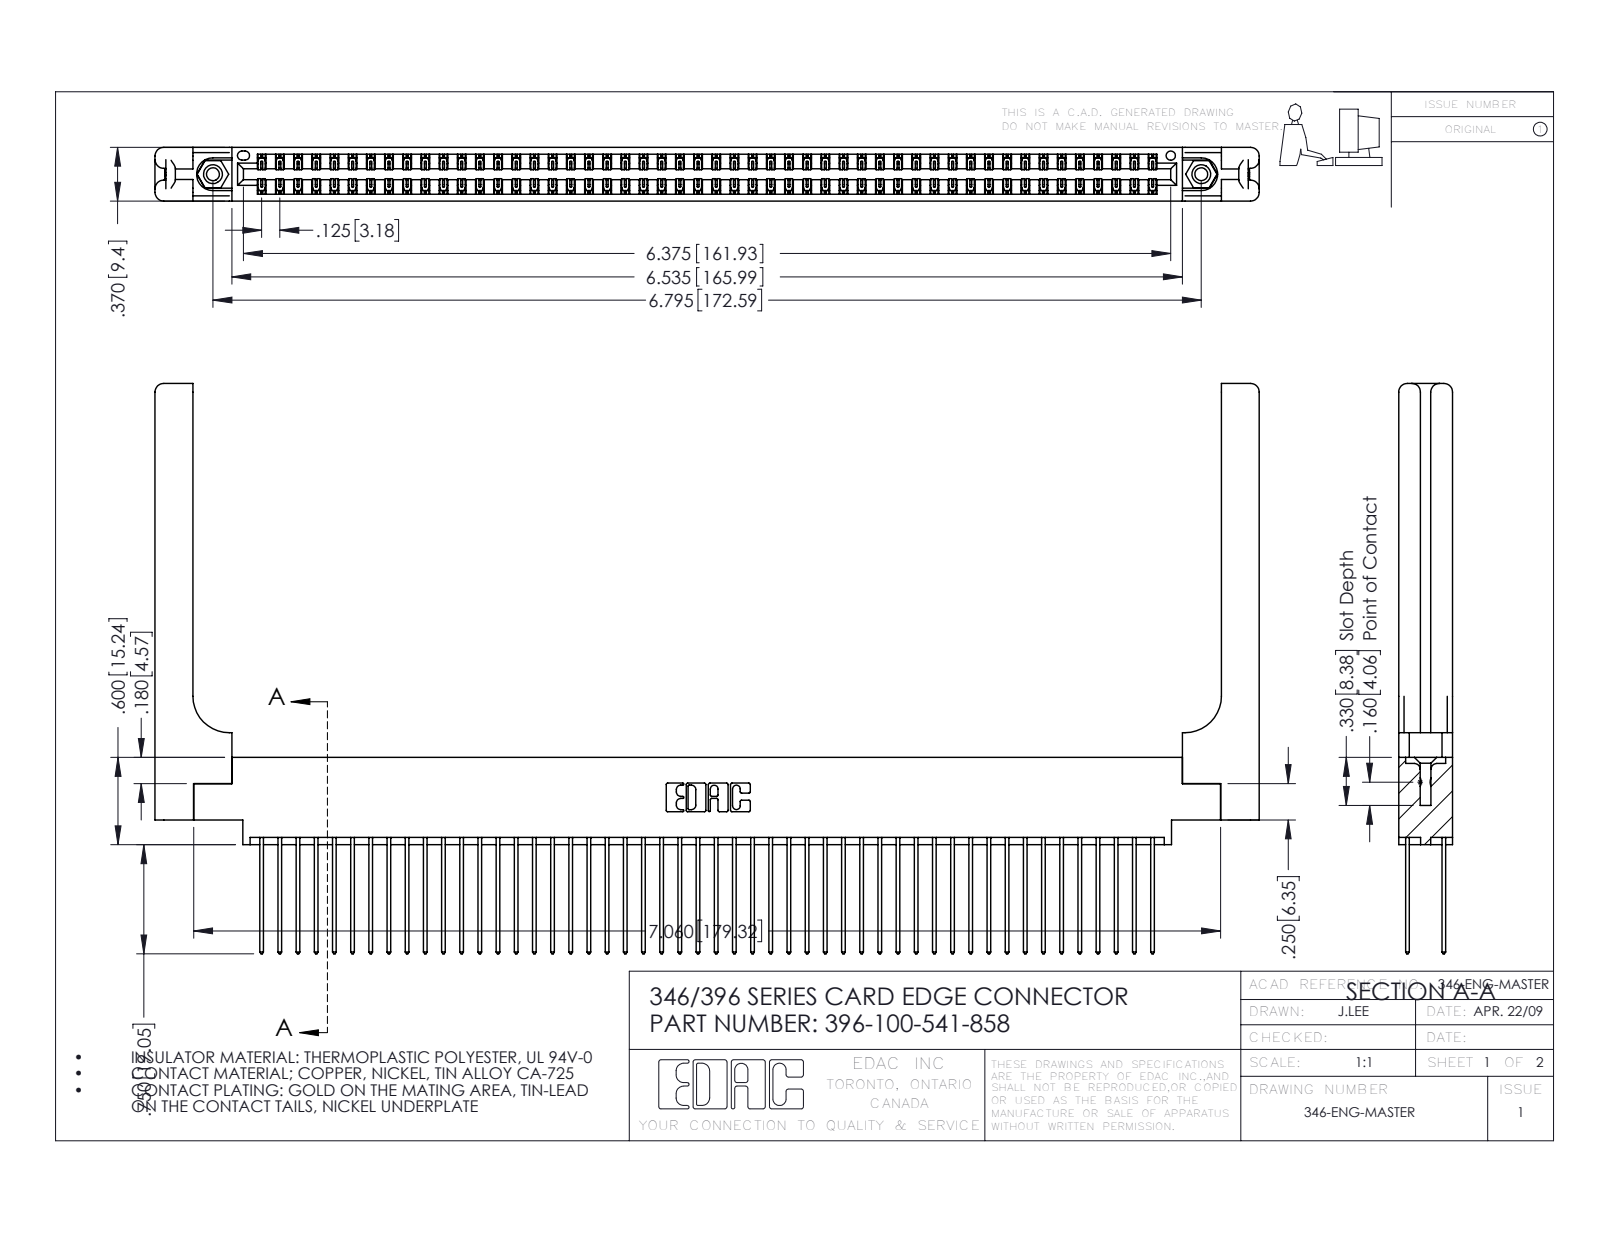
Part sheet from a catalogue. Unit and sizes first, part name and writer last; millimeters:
Units: millimetres
Overall size (bounding box): 192.8 × 99.6 × 9.4
Round holes (diameter × count): ⌀2.3 ×2, ⌀3.2 ×2, ⌀4 ×2, ⌀1.6 ×1
Round bosses / shafts (diameter × count): ⌀3.9 ×2
Partial cylindrical surfaces — rounded edges, fillets, slot ends (radius × count): R0.2 ×150, R0.3 ×100, R0.3 ×22, R1.5 ×16, R0.2 ×6, R0.8 ×6, R0.7 ×3, R0.4 ×2
Main face-to-face distances: 1.2, 8.2, 1.8, 9.4, 6.4, 0.6, 7.6, 7, 3.8, 3.8
Hole centre spacings: 6.2, 167.3, 172.6
Volume: 26 780 mm³ · Surface area: 34 540 mm²
Bodies: 105 solids, 5582 faces (3728 planar, 1794 cylindrical, 60 other)
Part name (STEP PRODUCT): 346 Part_0.170 Offset - 0.156 Dia-TH; 346-220-058_345-220-058; 345-292-001_345-293-141; 345-250-001_345-250-001-102 (+1 more)
STEP written by: SolidWorks 2016 (CONFIG_CONTROL_DESIGN)
